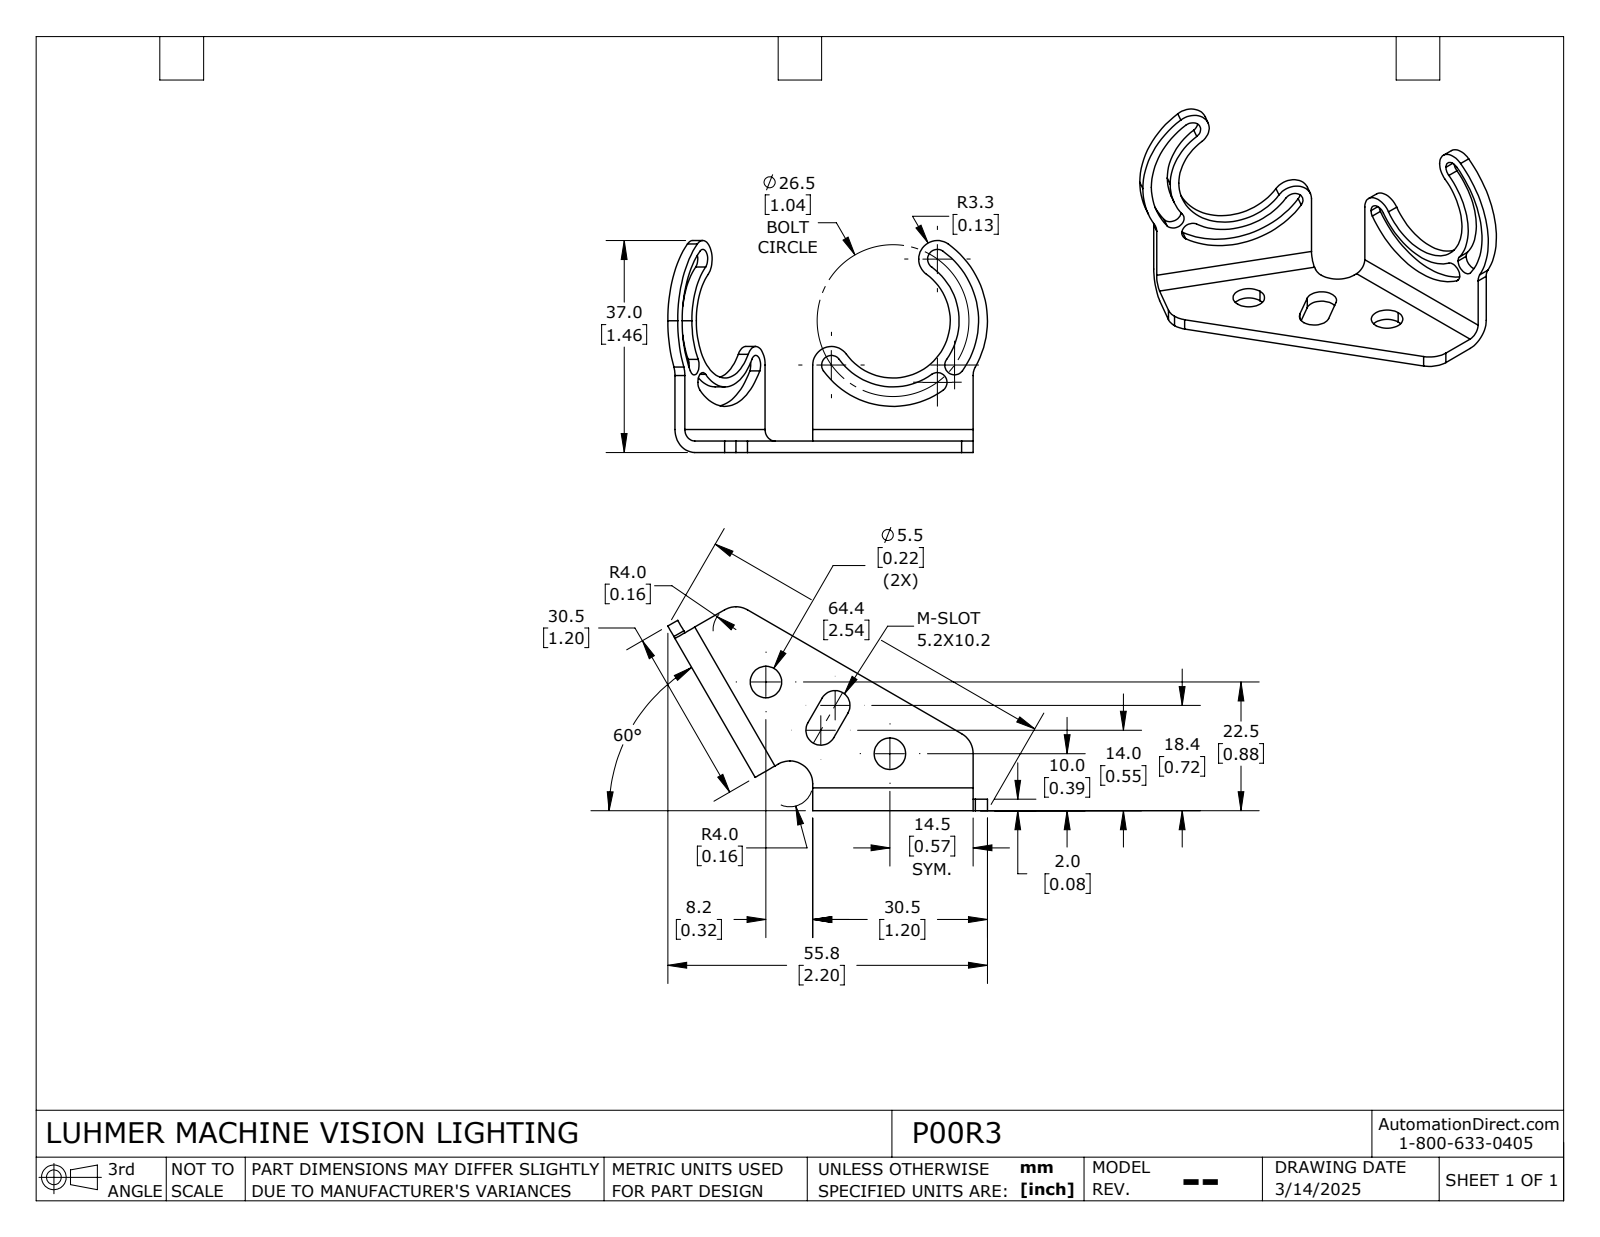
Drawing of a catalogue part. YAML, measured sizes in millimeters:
part_name: "P00R3"
step_written_by: "SolidWorks 2024 (AUTOMOTIVE_DESIGN)"
units: millimeters
bodies: {solids: 1, faces: 64, planar: 13, cylindrical: 51, other: 0}
overall_size: [55.8, 37, 35.6]
volume: 3160
surface_area: 4292
round_holes:
  - {diameter: 5.5, count: 2}
partial_cylinders:
  - {radius: 1.7, count: 8}
  - {radius: 4, count: 5}
  - {radius: 3.3, count: 4}
  - {radius: 2, count: 2}
  - {radius: 2.6, count: 2}
  - {radius: 3, count: 2}
  - {radius: 10, count: 2}
  - {radius: 11.6, count: 2}
face_to_face_distances: [2, 28, 5.2]
hole_center_spacings: [25]
